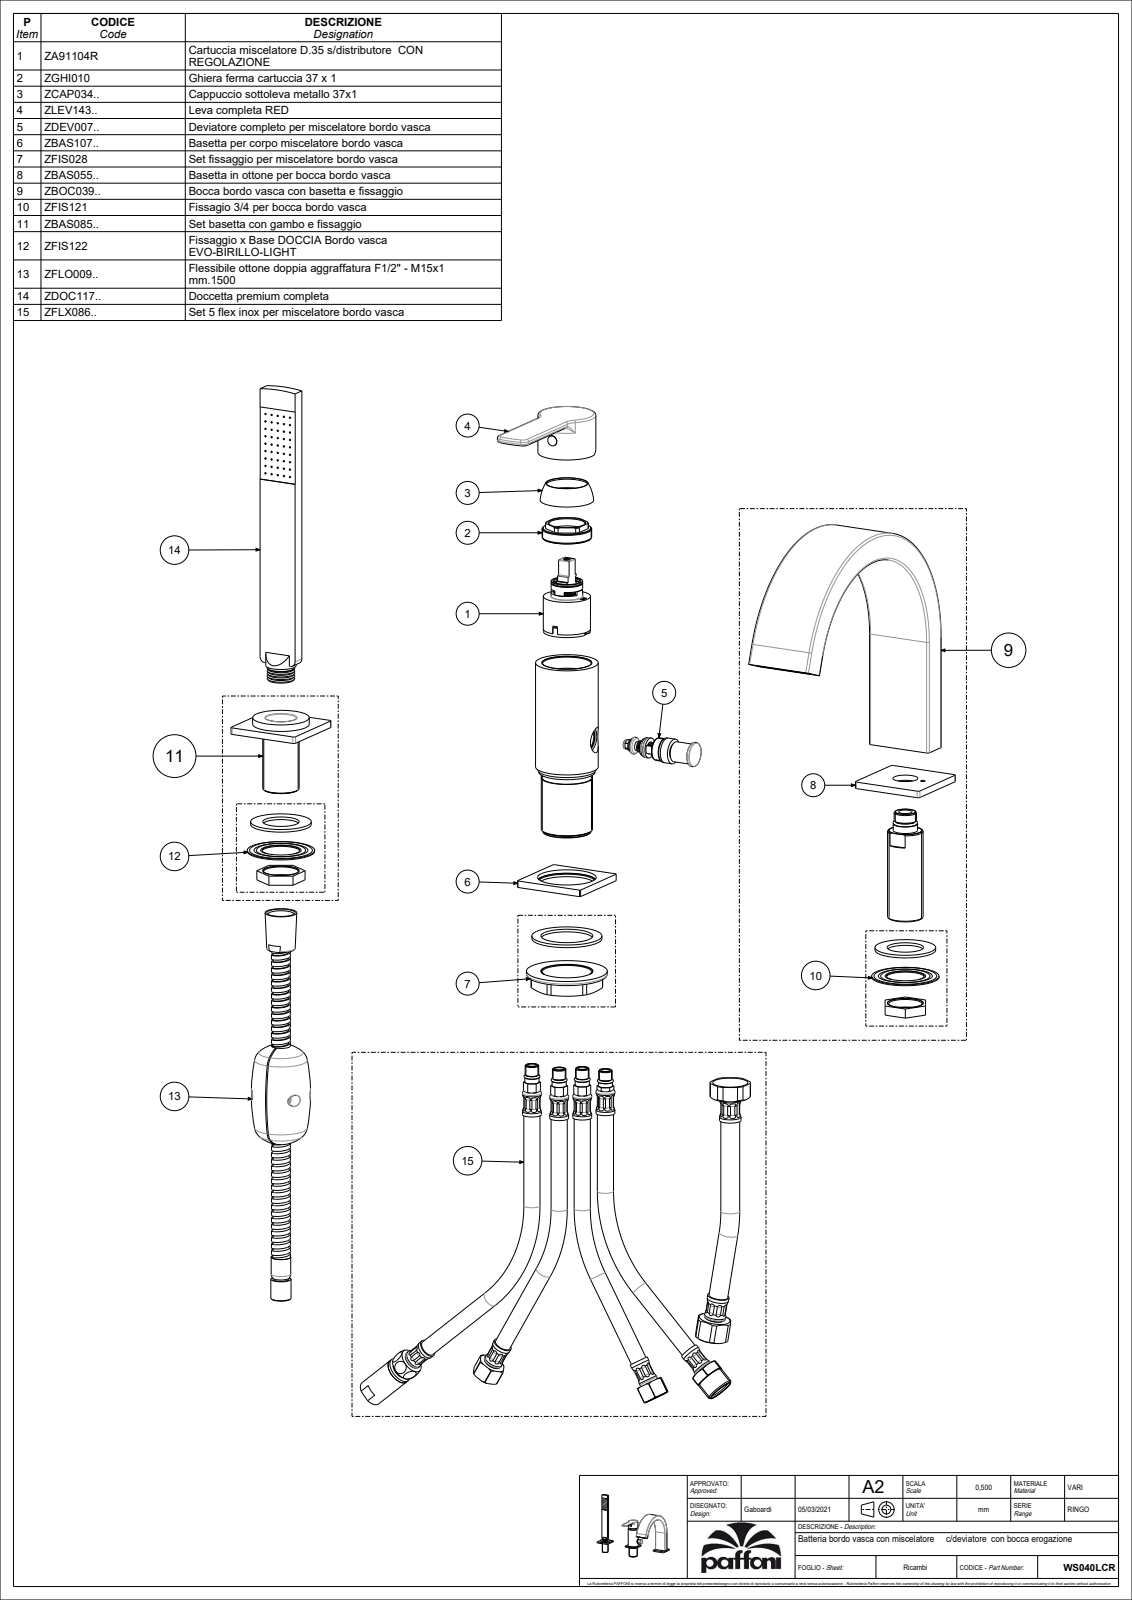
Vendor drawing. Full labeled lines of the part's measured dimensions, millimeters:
Part name (STEP PRODUCT): WS040LCR
STEP written by: CREO PARAMETRIC BY PTC INC, 2020044 (CONFIG_CONTROL_DESIGN)
Units: millimetres
Bodies: 6 solids, 1689 faces (960 planar, 436 cylindrical, 293 other)
Overall size (bounding box): 355 × 228 × 216.96
Volume: 413 255 mm³ · Surface area: 198 175 mm²
Round holes (diameter × count): ⌀7 ×6, ⌀3.3 ×2, ⌀4 ×2, ⌀4.5 ×2, ⌀10 ×2, ⌀48 ×2, ⌀3 ×1, ⌀3.1 ×1, ⌀3.4 ×1, ⌀4.3 ×1, ⌀5 ×1, ⌀6 ×1
Round bosses / shafts (diameter × count): ⌀2 ×11, ⌀42.5 ×2, ⌀15 ×2, ⌀46.5 ×1, ⌀44.2 ×1, ⌀43 ×1, ⌀42 ×1, ⌀38 ×1
Partial cylindrical surfaces — rounded edges, fillets, slot ends (radius × count): R0.5 ×66, R1.5 ×24, R0.15 ×11, R0.3 ×4, R1 ×2, R4 ×2, R5 ×2, R10 ×2
Main face-to-face distances: 3.5, 5, 47.5, 15, 1.5, 16.5, 11.5, 51, 10, 44
Hole centre spacings: 3, 8.6, 10.63, 14, 14.32, 143.09, 143.22, 150
